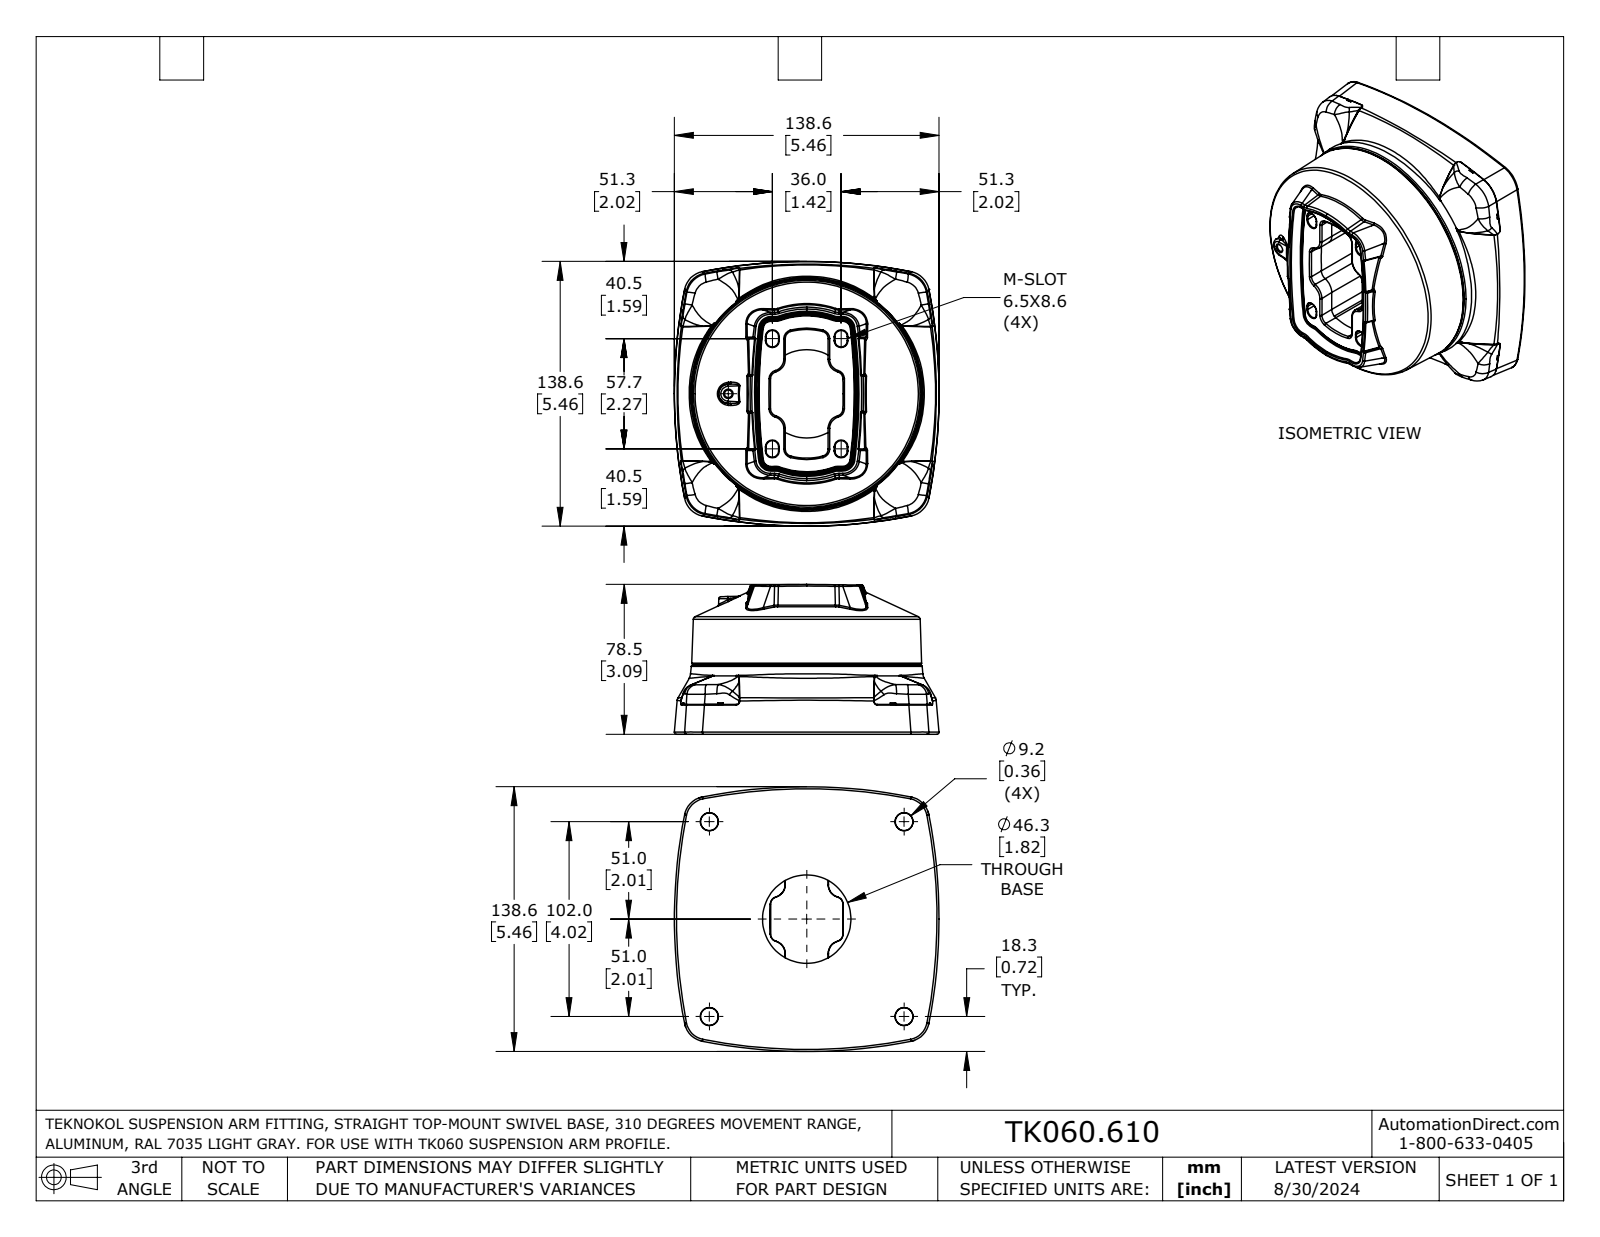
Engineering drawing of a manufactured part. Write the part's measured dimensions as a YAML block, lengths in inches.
part_name: "TK060.610"
step_written_by: "SolidWorks 2023 (AUTOMOTIVE_DESIGN)"
units: inches
bodies: {solids: 1, faces: 1104, planar: 222, cylindrical: 159, other: 723}
overall_size: [5.458, 5.458, 3.09]
volume: 47.32
surface_area: 144.8
round_holes:
  - {diameter: 0.142, count: 8}
  - {diameter: 0.157, count: 1}
  - {diameter: 1.822, count: 1}
round_bosses_or_shafts:
  - {diameter: 0.141, count: 8}
  - {diameter: 4.685, count: 1}
partial_cylinders:
  - {radius: 0.02, count: 32}
  - {radius: 0.022, count: 32}
  - {radius: 0.014, count: 8}
  - {radius: 0.055, count: 8}
  - {radius: 0.056, count: 8}
  - {radius: 0.148, count: 8}
  - {radius: 0.155, count: 8}
  - {radius: 0.031, count: 4}
face_to_face_distances: [2.805, 1.438, 1.367, 0.614, 0.824, 2.191, 2.226, 1.612, 0.787, 0.579]
hole_center_spacings: [3.876, 2.741, 0.92, 5.404, 1.702, 2.236, 2.741, 3.17]
